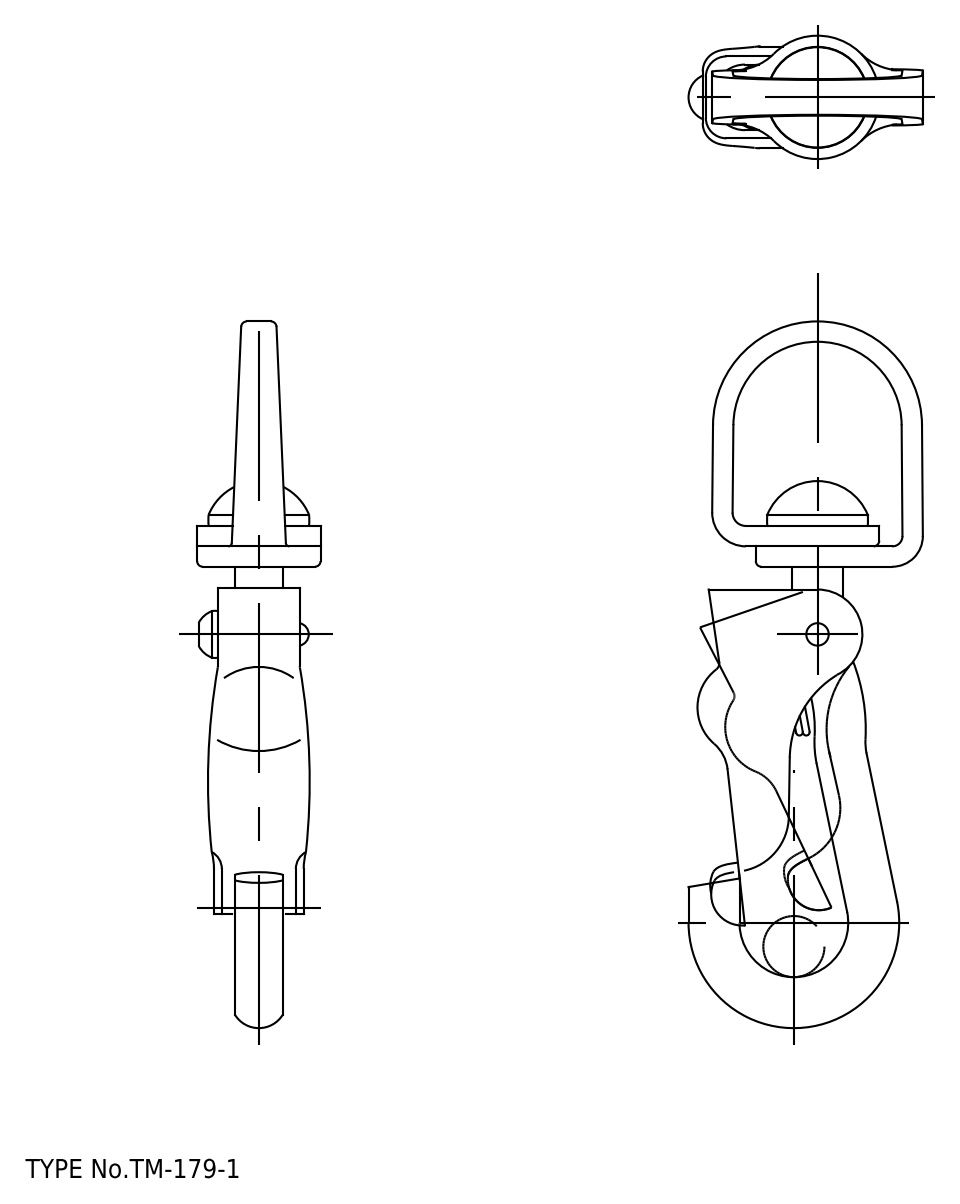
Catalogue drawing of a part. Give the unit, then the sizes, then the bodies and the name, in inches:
Units: inches
Overall size (bounding box): 4.094 × 1.357 × 0.715
Round holes (diameter × count): ⌀0.13 ×1, ⌀0.394 ×1
Round bosses / shafts (diameter × count): ⌀0.715 ×1
Partial cylindrical surfaces — rounded edges, fillets, slot ends (radius × count): R0.138 ×6, R0.118 ×5, R0.047 ×4, R0.079 ×4, R0.329 ×4, R0.046 ×3, R0.177 ×3, R0.032 ×2
Main face-to-face distances: 0.047, 0.428, 0.236, 0.118, 0.475, 0.38, 0.048, 0.1, 0.375, 0.052
Volume: 0.623 in³ · Surface area: 14.04 in²
Bodies: 3 solids, 165 faces (38 planar, 73 cylindrical, 54 other)
Part name (STEP PRODUCT): Dカン; フック; レバー
STEP written by: spGate 20.6.3 (****-****-****-****) (AUTOMOTIVE_DESIGN)
